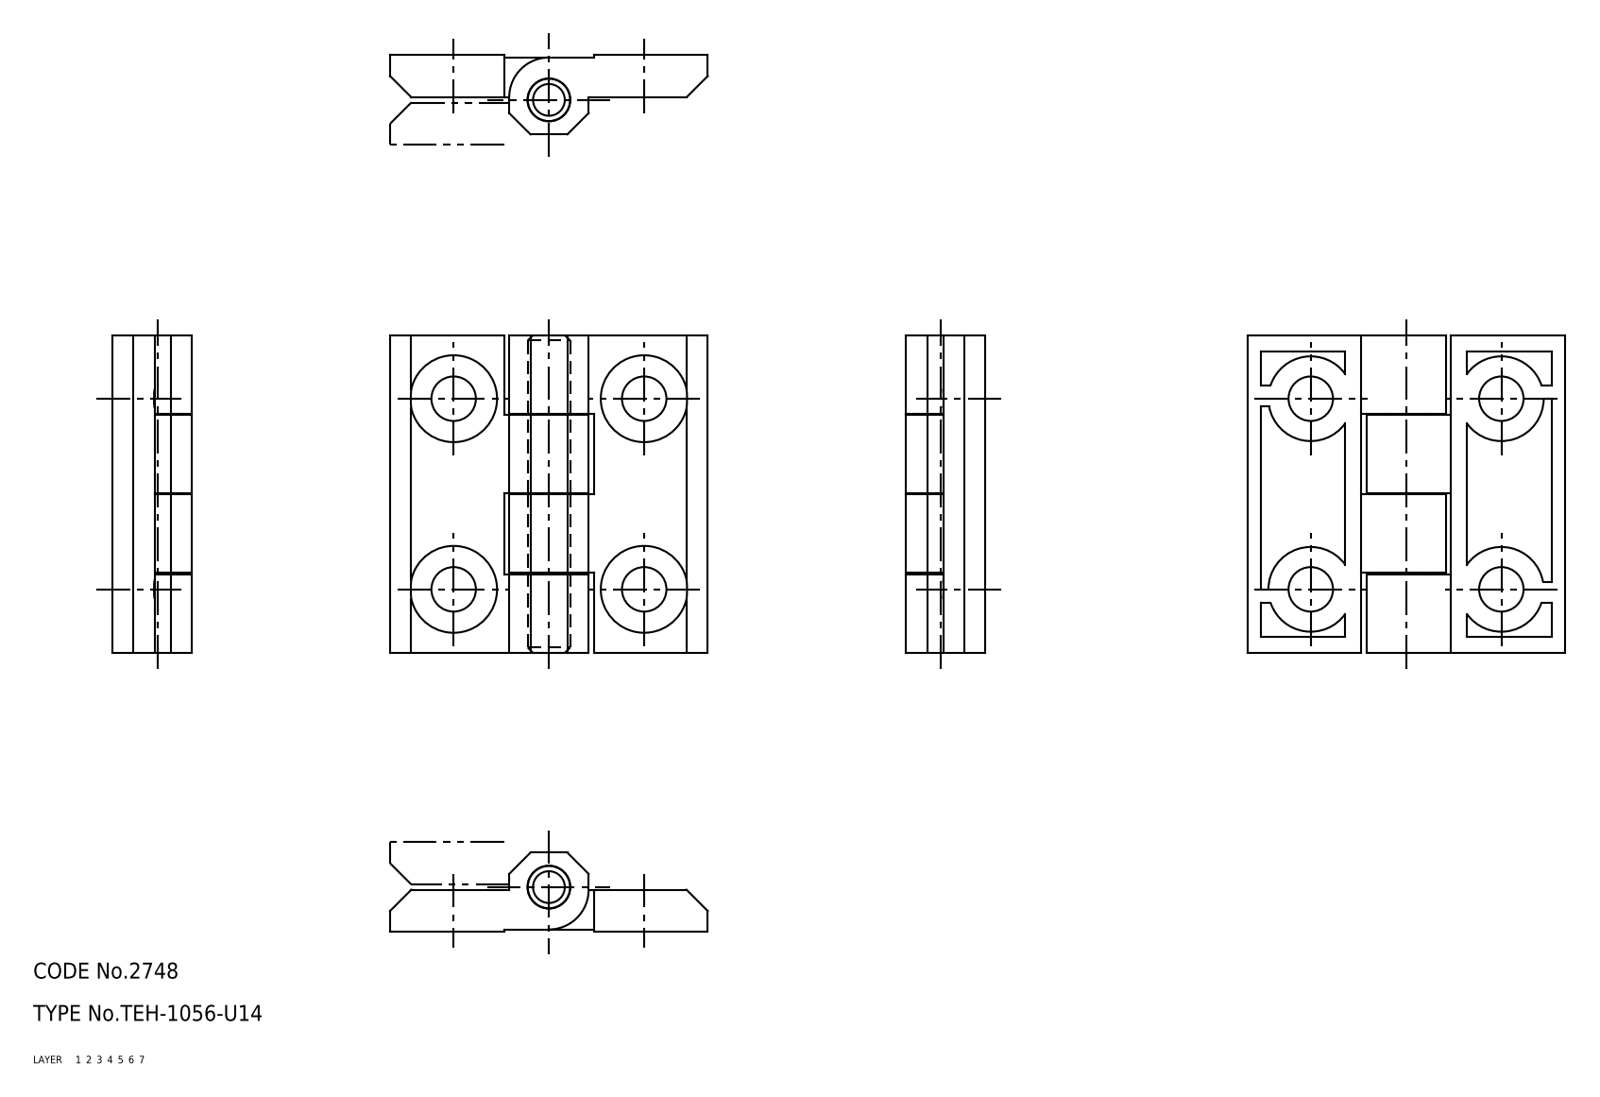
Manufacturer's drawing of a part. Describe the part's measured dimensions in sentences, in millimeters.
The part is named "shaft; hinge pieces_B; hinge pieces_A; TEH_1056_U14_2886_36". Its 3-D file was written by "CADfix (AUTOMOTIVE_DESIGN)". It is 3 solids with 118 faces: 0 planar, 0 cylindrical and 118 other. Overall it measures 60 by 60 by 15 millimeters. Its volume is 24 636 cubic millimeters and its surface area 15 759 square millimeters.
